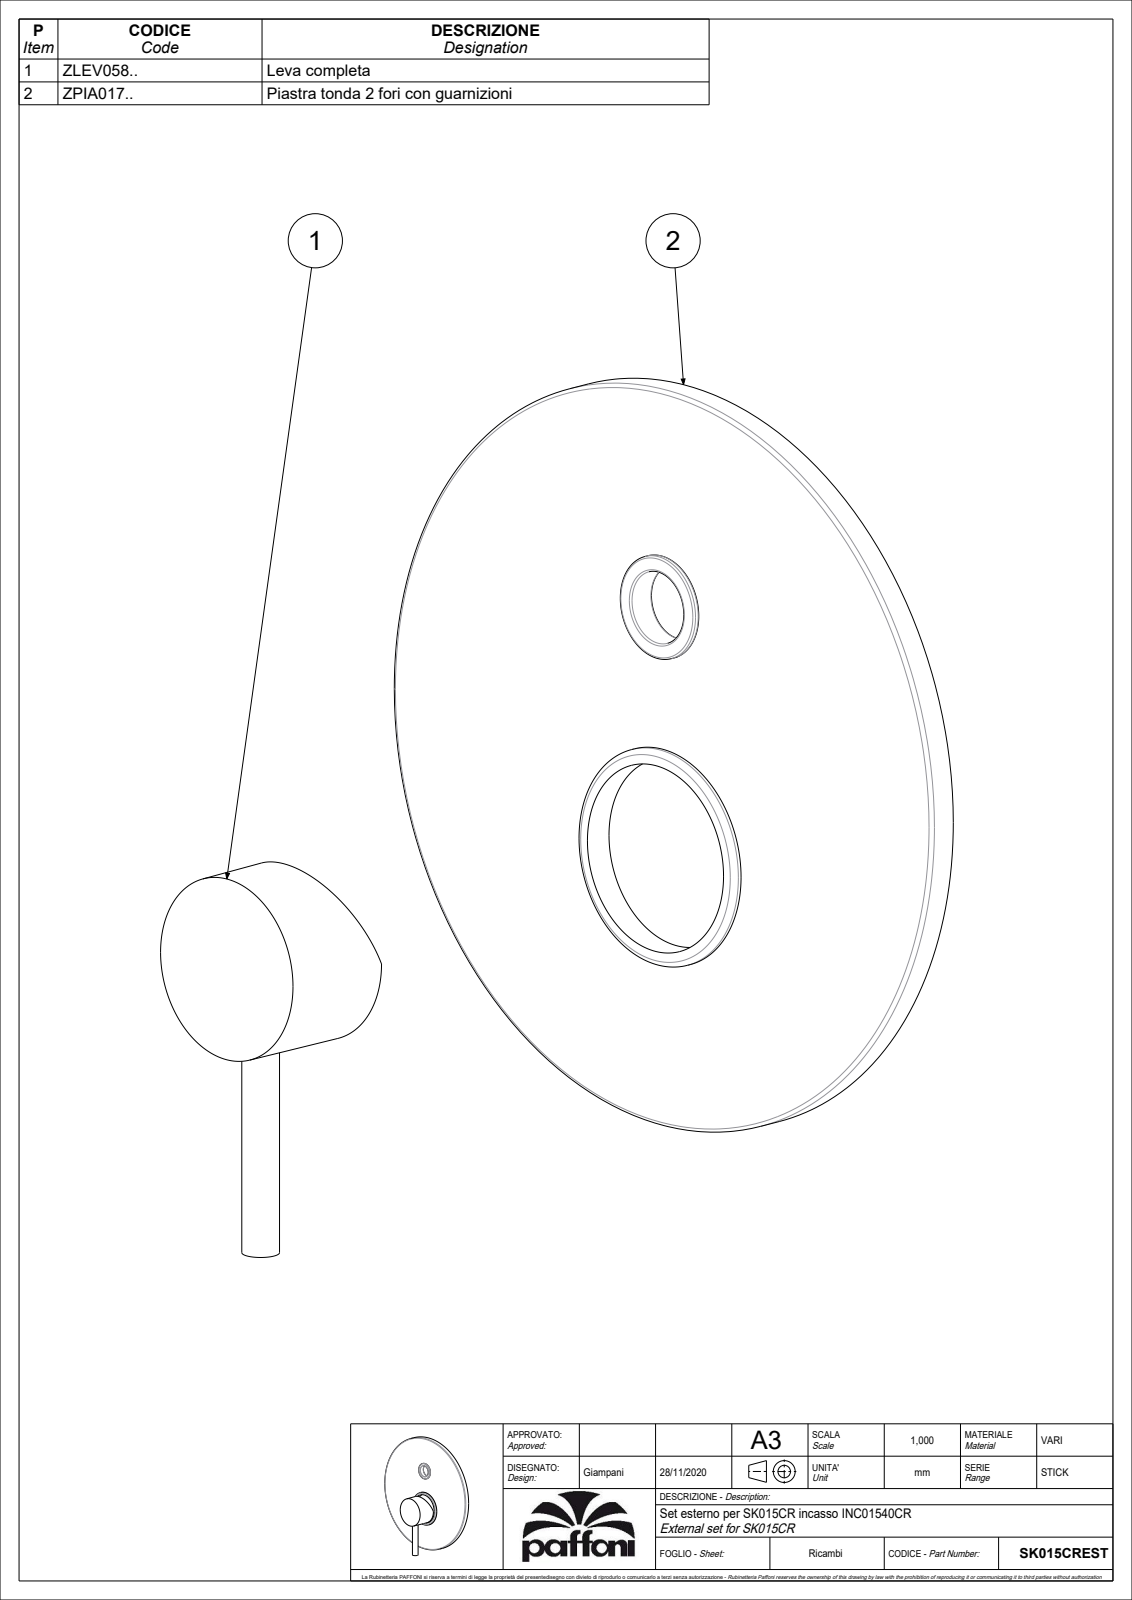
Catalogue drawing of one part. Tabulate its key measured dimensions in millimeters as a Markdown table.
| quantity | value |
| --- | --- |
| part name | SK015CREST |
| STEP written by | CREO PARAMETRIC BY PTC INC, 2020044 (CONFIG_CONTROL_DESIGN) |
| units | millimeters |
| bodies | 2 solids, 115 faces (46 planar, 31 cylindrical, 38 other) |
| overall size | 206.1 × 200 × 46 |
| volume | 162 773 mm³ |
| surface area | 94 830 mm² |
| round holes (diameter × count) | 3.3 × 1, 4.2 × 1, 10 × 1, 19.1 × 1, 50.5 × 1, 145 × 1, 198 × 1 |
| round bosses / shafts (diameter × count) | 200 × 1, 195 × 1, 58.5 × 1, 54 × 1, 25.1 × 1, 23.5 × 1, 9.9 × 1, 5 × 1 |
| partial cylindrical surfaces (radius × count) | 6.5 × 1 |
| main face-to-face distances | 1, 8, 9, 35, 43, 34, 7, 42, 2, 2.5 |
| hole center spacings | 26.75, 41.25, 68 |
